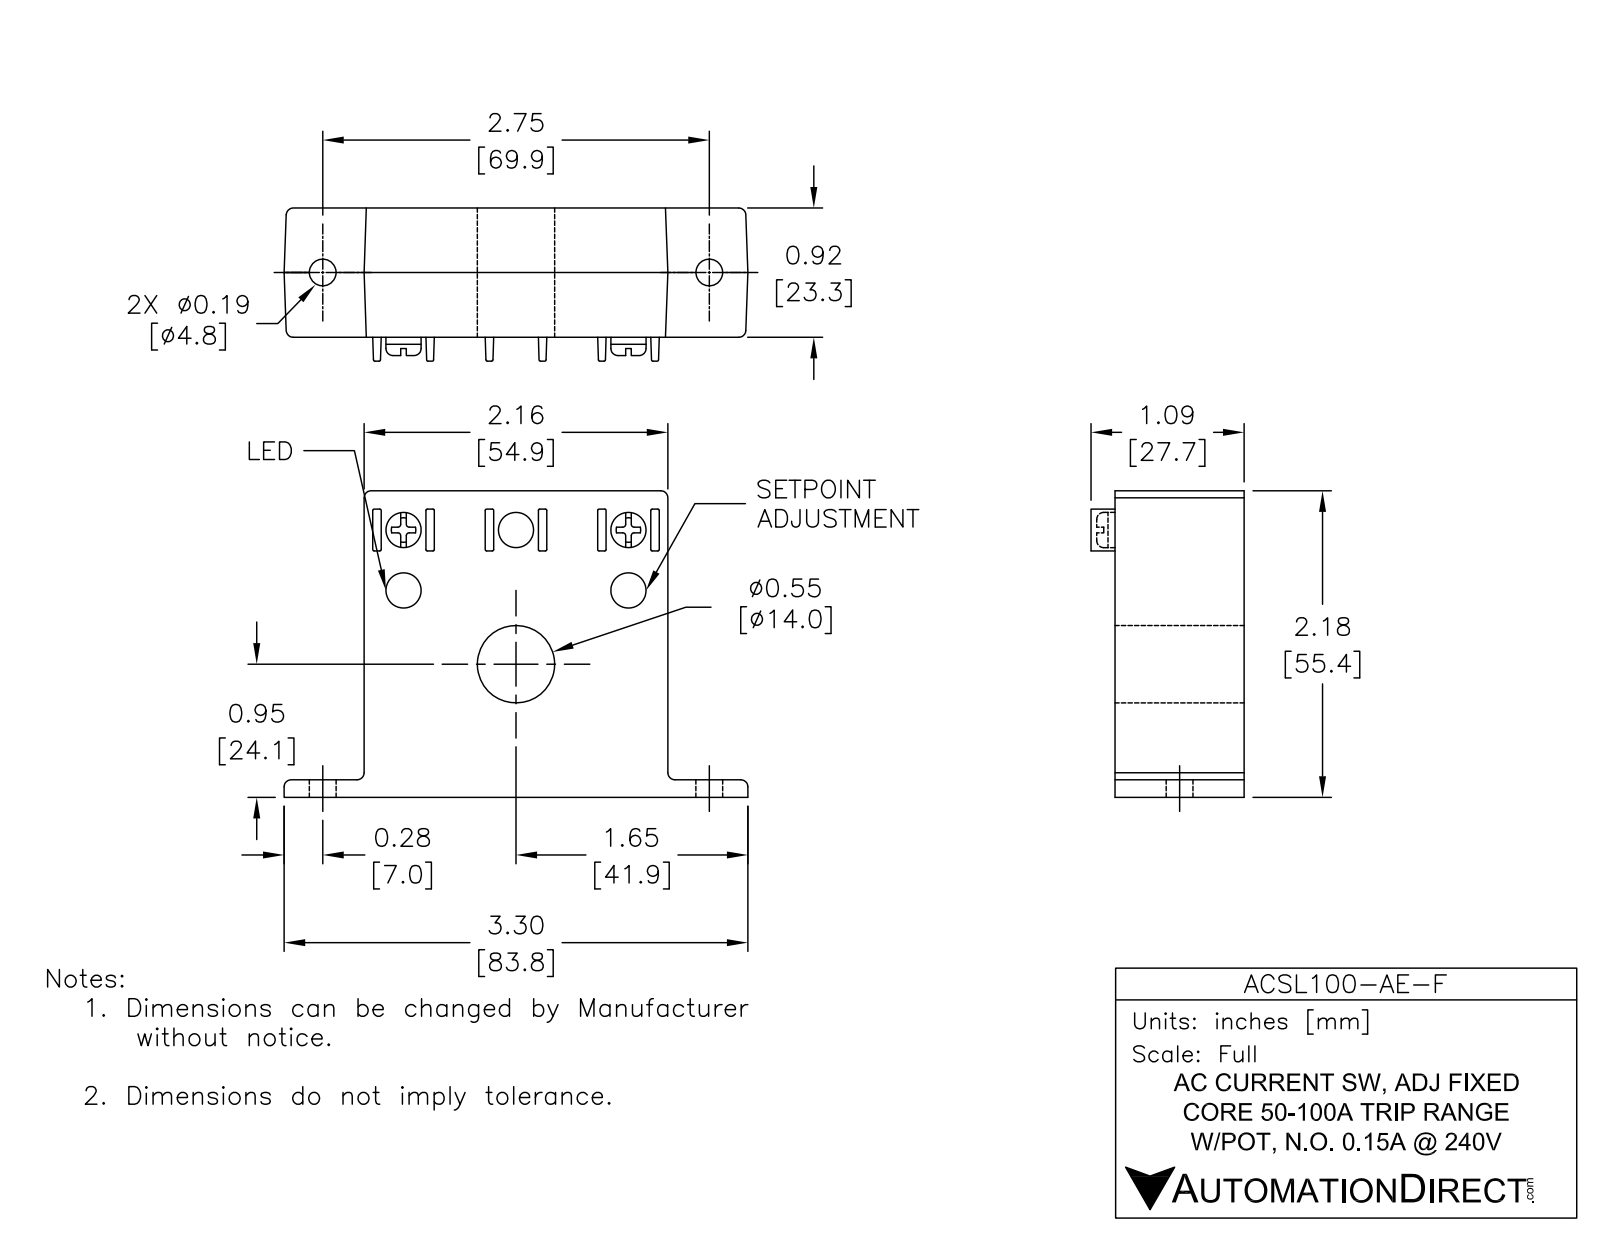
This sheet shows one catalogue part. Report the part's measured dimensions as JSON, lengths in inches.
{"part_name": "ACSL100-AE-F", "step_written_by": "SolidWorks 2018 (AUTOMOTIVE_DESIGN)", "units": "inches", "bodies": {"solids": 10, "faces": 368, "planar": 236, "cylindrical": 114, "other": 18}, "overall_size": [3.292, 2.188, 1.151], "volume_in3": 4.41, "surface_area_in2": 30.46, "round_holes": [[0.2, 4], [0.121, 2], [0.13, 2], [0.14, 2], [0.24, 2], [0.55, 1], [0.59, 1]], "round_bosses_or_shafts": [[0.321, 2], [0.138, 2], [0.187, 1], [0.063, 1]], "partial_cylinders_radius": [[0.015, 14], [0.089, 1]], "face_to_face_distances": [0.937, 0.938, 2.188, 2.172, 0.145, 2.043, 0.031, 0.383, 0.062, 0.824], "hole_center_spacings": [0.341, 1.036, 1.272, 1.647, 1.682, 0.015, 0.335, 1.034]}
